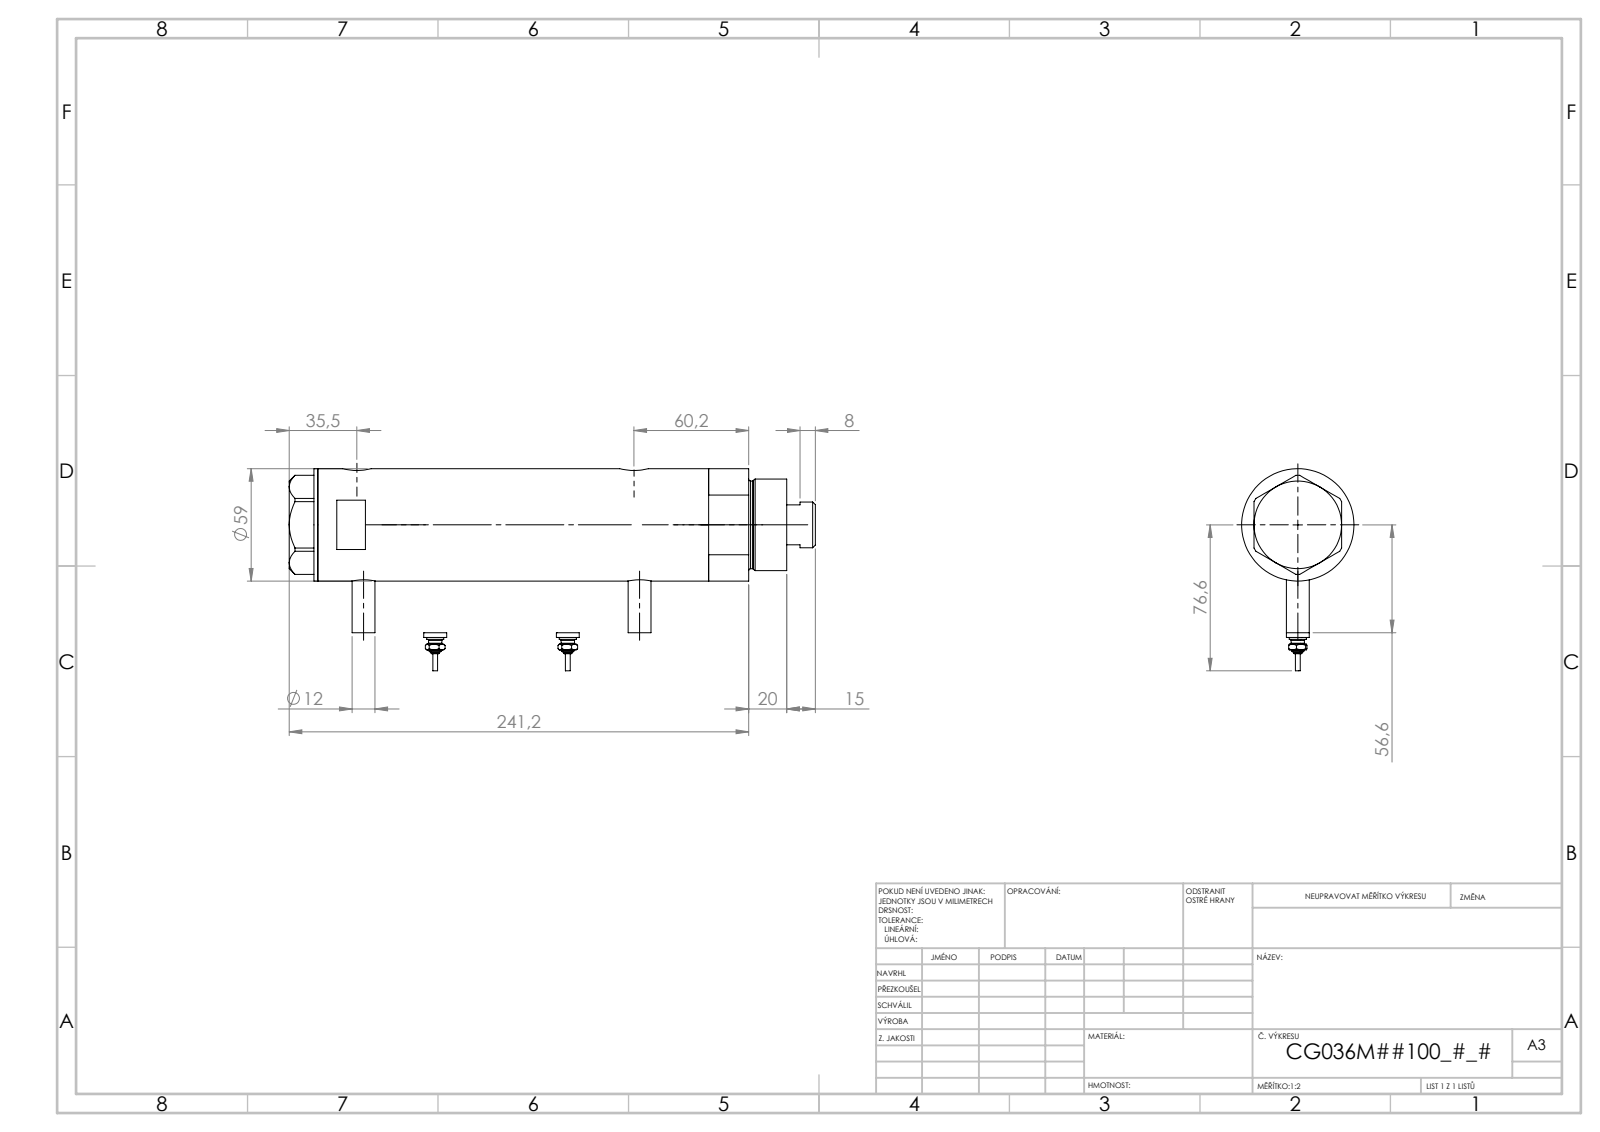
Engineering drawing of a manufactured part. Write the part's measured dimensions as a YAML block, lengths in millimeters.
part_name: "V270CG_MIDDLE; V270CG_BACK; V270CG_FRONT; V270CG_SWITCH (+1 more)"
step_written_by: "SolidWorks 2019 (CONFIG_CONTROL_DESIGN)"
units: millimeters
bodies: {solids: 6, faces: 232, planar: 81, cylindrical: 77, other: 74}
overall_size: [263.42, 91.3, 59]
volume: 594695
surface_area: 121539
round_holes:
  - {diameter: 5, count: 2}
  - {diameter: 9.73, count: 2}
  - {diameter: 12.5, count: 2}
  - {diameter: 15, count: 2}
  - {diameter: 8.5, count: 1}
  - {diameter: 25, count: 1}
  - {diameter: 26.5, count: 1}
  - {diameter: 36, count: 1}
  - {diameter: 40, count: 1}
  - {diameter: 52, count: 1}
round_bosses_or_shafts:
  - {diameter: 12, count: 4}
  - {diameter: 9, count: 2}
  - {diameter: 7, count: 2}
  - {diameter: 4.34, count: 2}
  - {diameter: 2.4, count: 2}
  - {diameter: 59, count: 1}
  - {diameter: 48, count: 1}
  - {diameter: 46, count: 1}
face_to_face_distances: [157.34, 23.5, 133.84, 15, 38.5, 172.34, 248.42, 233.42, 209.92, 76.08]
hole_center_spacings: [2.9, 3.5, 132.15, 135.05, 135.65, 138.55, 2.89, 2.91]
